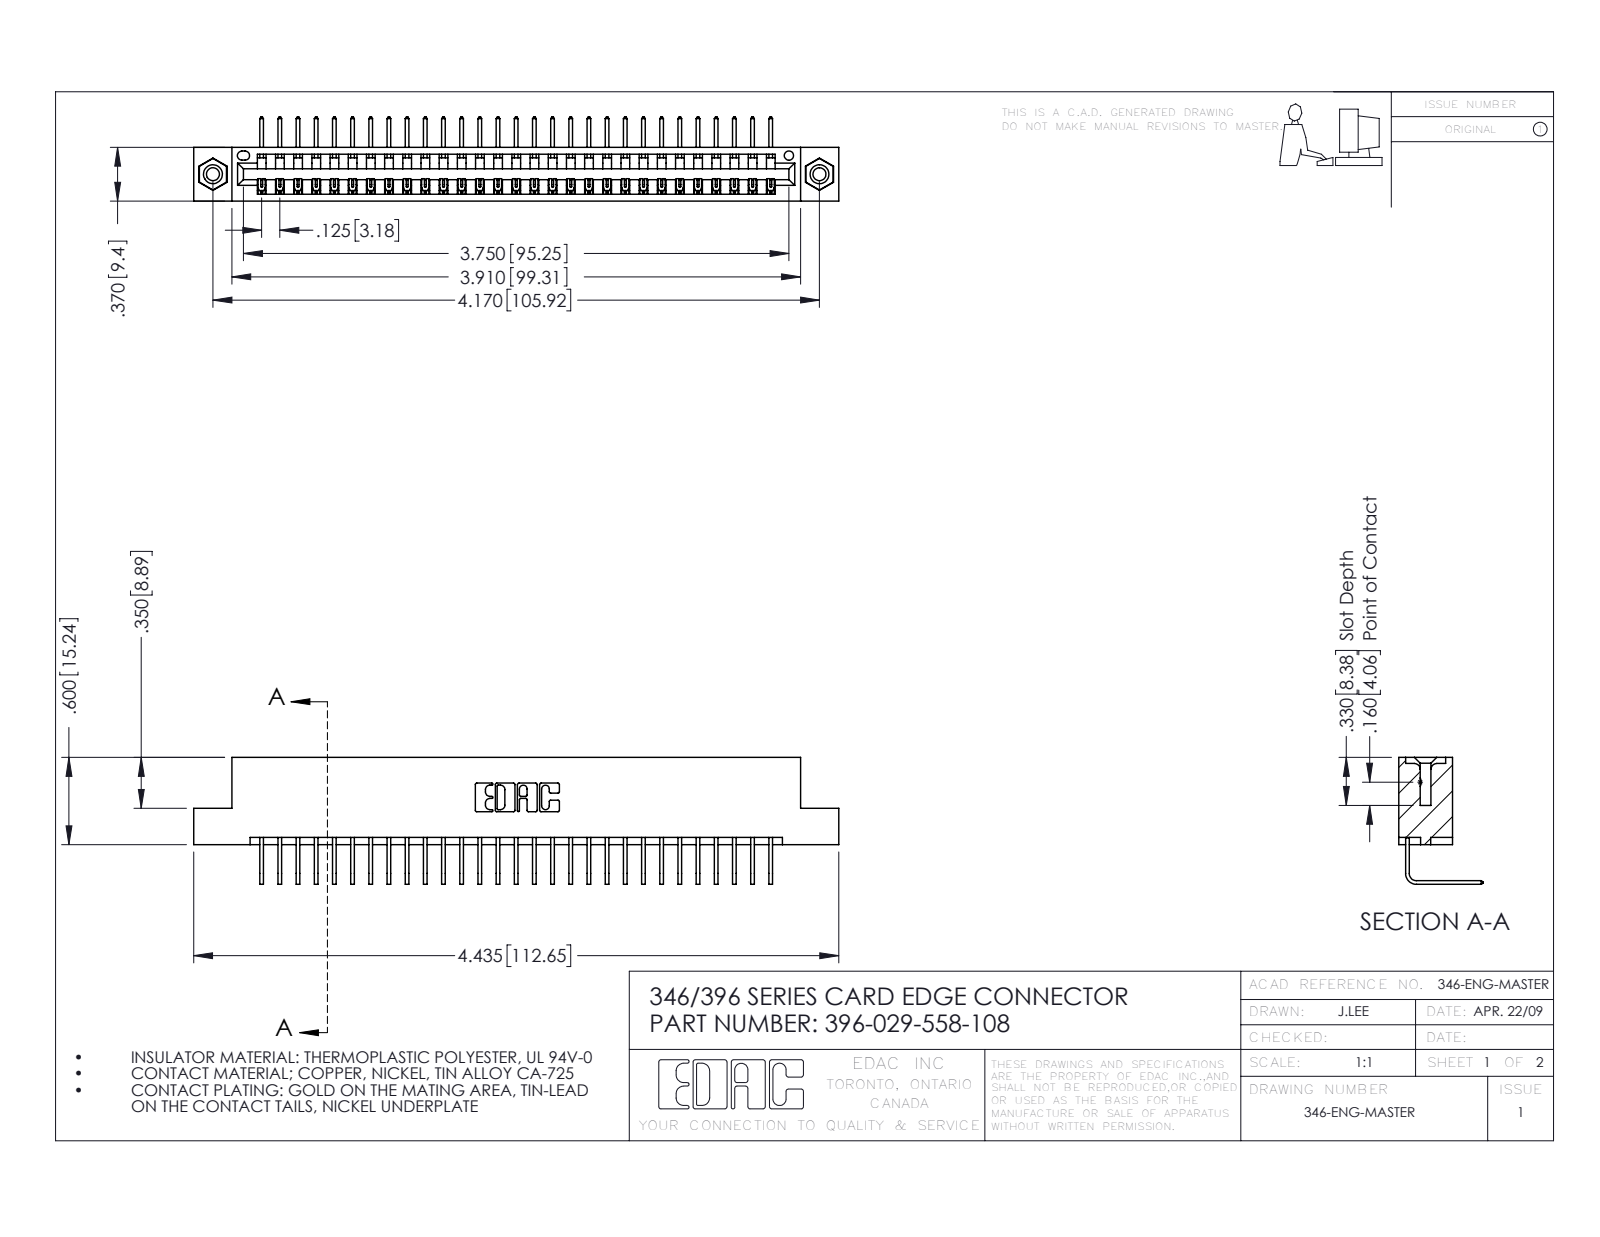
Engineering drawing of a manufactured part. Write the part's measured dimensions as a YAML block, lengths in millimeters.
part_name: "396-029-558-108; 346 Part_Flush Mounting Lugs - 0.156 Dia-TI; 345-292-001_558 Tail - 2; 345-250-001_345-250-003-102"
step_written_by: "SolidWorks 2016 (CONFIG_CONTROL_DESIGN)"
units: millimeters
bodies: {solids: 32, faces: 1922, planar: 1326, cylindrical: 580, other: 16}
overall_size: [112.6, 22.2, 14.7]
volume: 10800
surface_area: 13940
round_holes:
  - {diameter: 2.3, count: 2}
  - {diameter: 3.2, count: 2}
  - {diameter: 4, count: 2}
  - {diameter: 1.6, count: 1}
round_bosses_or_shafts:
  - {diameter: 3.9, count: 2}
partial_cylinders:
  - {radius: 0.2, count: 58}
  - {radius: 0.3, count: 22}
  - {radius: 0.2, count: 6}
  - {radius: 0.8, count: 6}
  - {radius: 0.7, count: 3}
  - {radius: 0.8, count: 2}
  - {radius: 1, count: 2}
  - {radius: 0.4, count: 1}
face_to_face_distances: [8.2, 1.2, 9.4, 6.4, 7.6, 0.6, 1.8, 3.8, 5.6, 2.5]
hole_center_spacings: [6.2, 100.6, 105.9]
